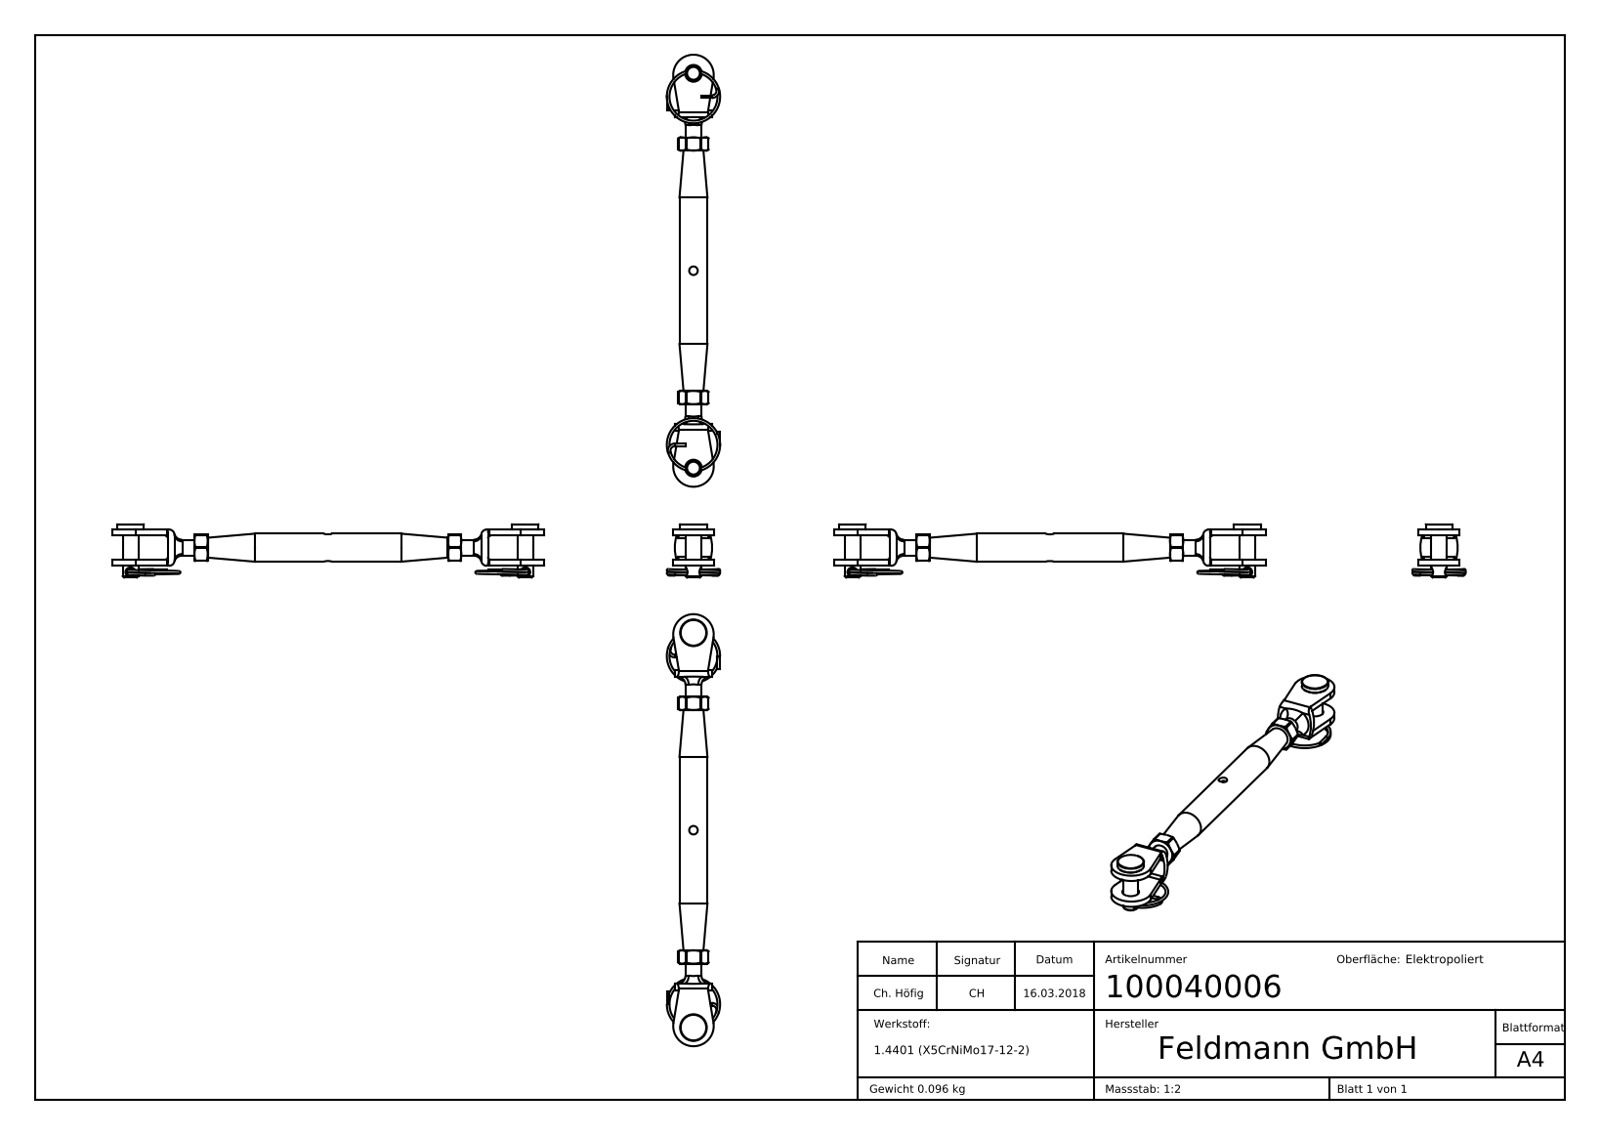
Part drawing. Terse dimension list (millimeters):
name: DIN 934 M4-M20_58321-240-6; 10005800X Teil2_100058006 Teil2; 10004000X Linksgewinde_100059006; 10005800X Teil1_100058006 Teil1 (+8 more)
written by: SolidWorks 2015 (CONFIG_CONTROL_DESIGN)
unit: mm
bodies: 9 solids, 451 faces (128 planar, 122 cylindrical, 201 other)
size: 162.2 × 20 × 20
volume: 11 981 mm³; area: 12 455 mm²
holes: 2× ⌀3, 2× ⌀6.3, 1× ⌀3.2, 1× ⌀5, 1× ⌀7.5
bosses: 4× ⌀1, 2× ⌀10, 2× ⌀5.8, 1× ⌀10.5, 1× ⌀6
rounds: 6× R0.5, 4× R0.4, 4× R1, 4× R2, 2× R7.6, 2× R16.16, 1× R3.85
face distances: 2.3, 11.3, 13.6, 9, 10, 2, 15.6, 13.3, 4.3, 5
hole spacings: 74.1, 148.2
